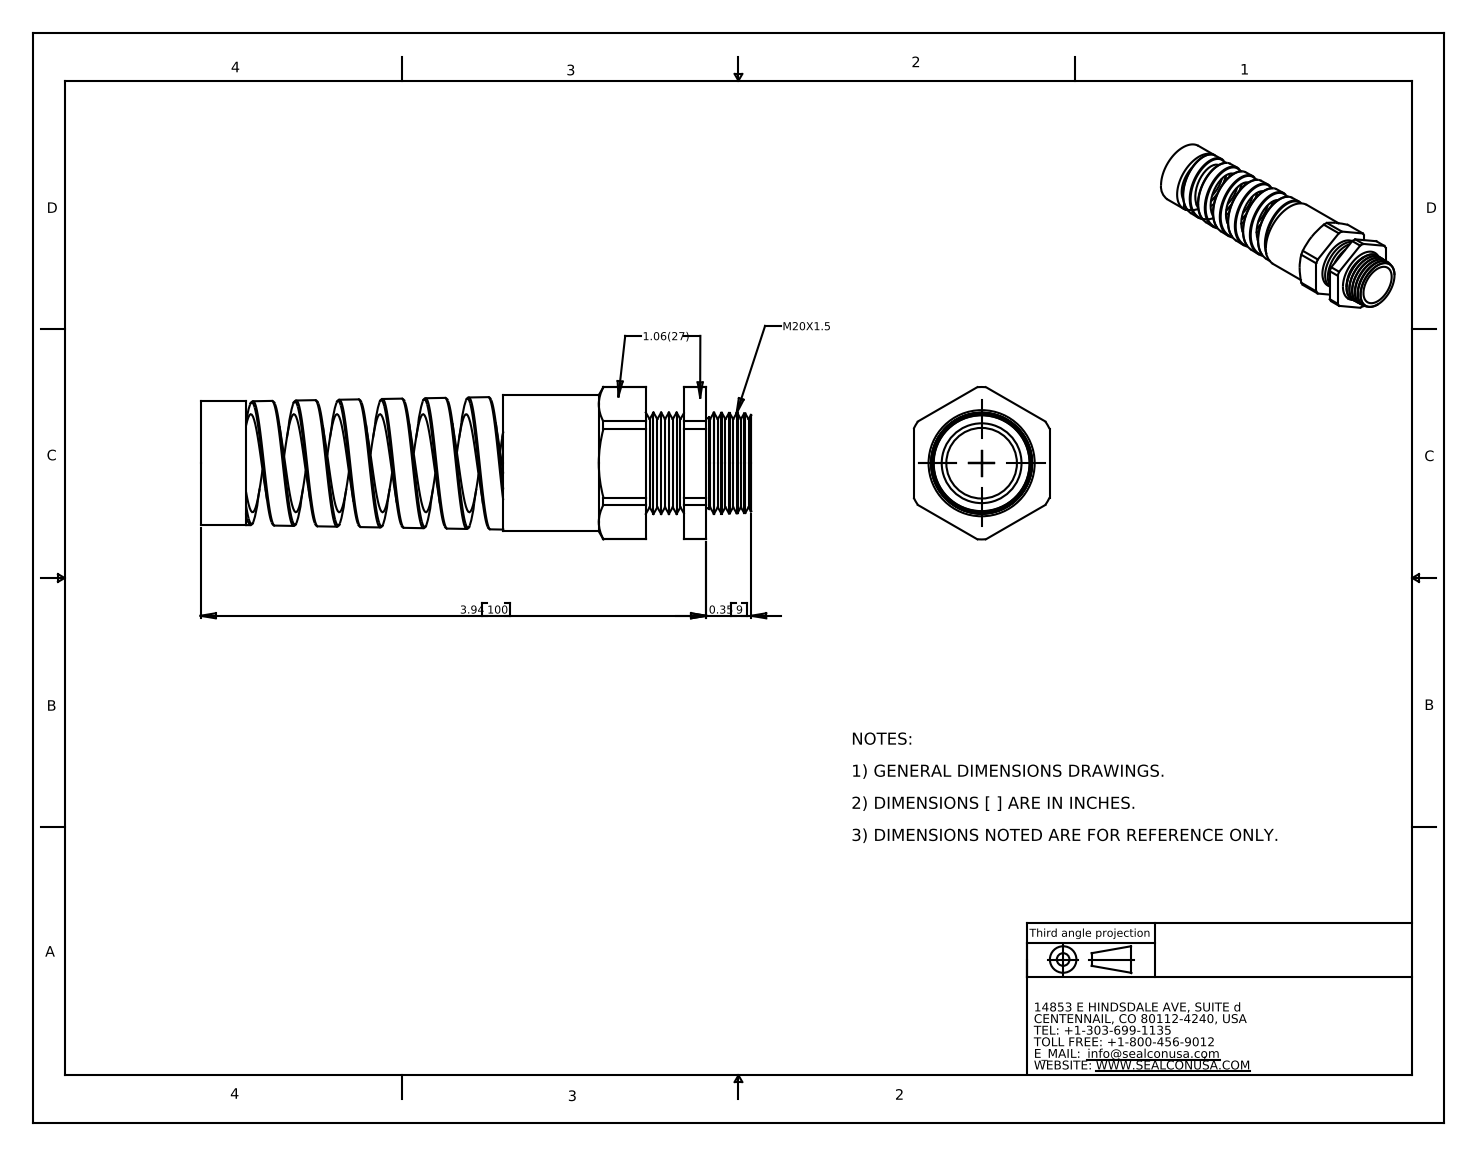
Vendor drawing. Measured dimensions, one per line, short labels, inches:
name: CF22MA-GY
written by: SolidWorks 2007 (CONFIG_CONTROL_DESIGN)
unit: in
bodies: 1 solid, 139 faces (19 planar, 34 cylindrical, 86 other)
size: 4.29 × 1.187 × 1.06
volume: 1.406 in³; area: 24.95 in²
holes: 1× ⌀0.55, 1× ⌀0.764, 1× ⌀0.79
bosses: 1× ⌀1.06, 1× ⌀0.964
rounds: 1× R0.594
face distances: 1.06, 0.297, 1.111, 1.407, 1.581, 0.471, 0.174, 2.359, 3.469, 3.766
